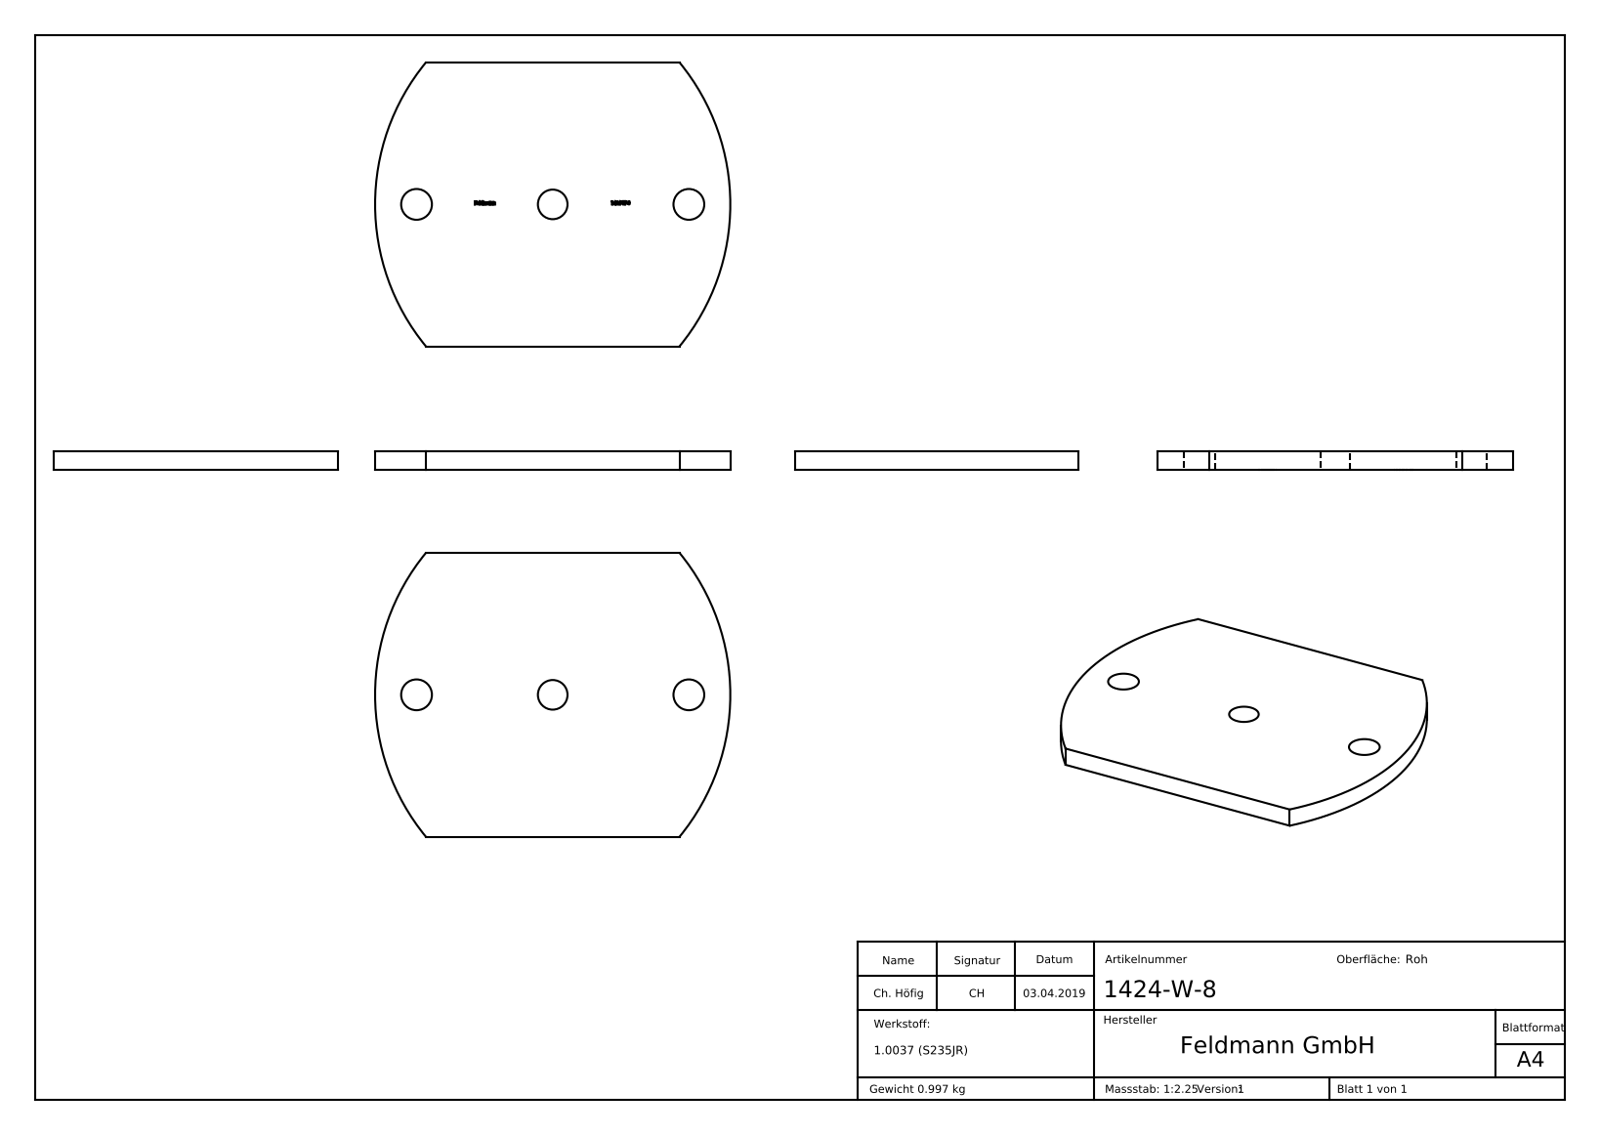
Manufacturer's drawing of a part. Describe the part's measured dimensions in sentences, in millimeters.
The part is named "1424-W-8". Its 3-D file was written by "SolidWorks 2015 (CONFIG_CONTROL_DESIGN)". It is 1 solid with 219 faces: 140 planar, 8 cylindrical and 71 other. Overall it measures 150 by 120 by 8 millimeters. Its volume is 127 828 cubic millimeters and its surface area 36 726 square millimeters. Round holes: 2 of diameter 13, 1 of diameter 12.5. Partial cylindrical surfaces (rounded edges, fillets, slot ends): 2 of radius 94.47. The main face-to-face distances are 8, 120, 7.9, 2.03, 0.54, 55.98, 59.37, 1.12, 59.24, 58.01. The hole center spacings are 57.5, 115.
